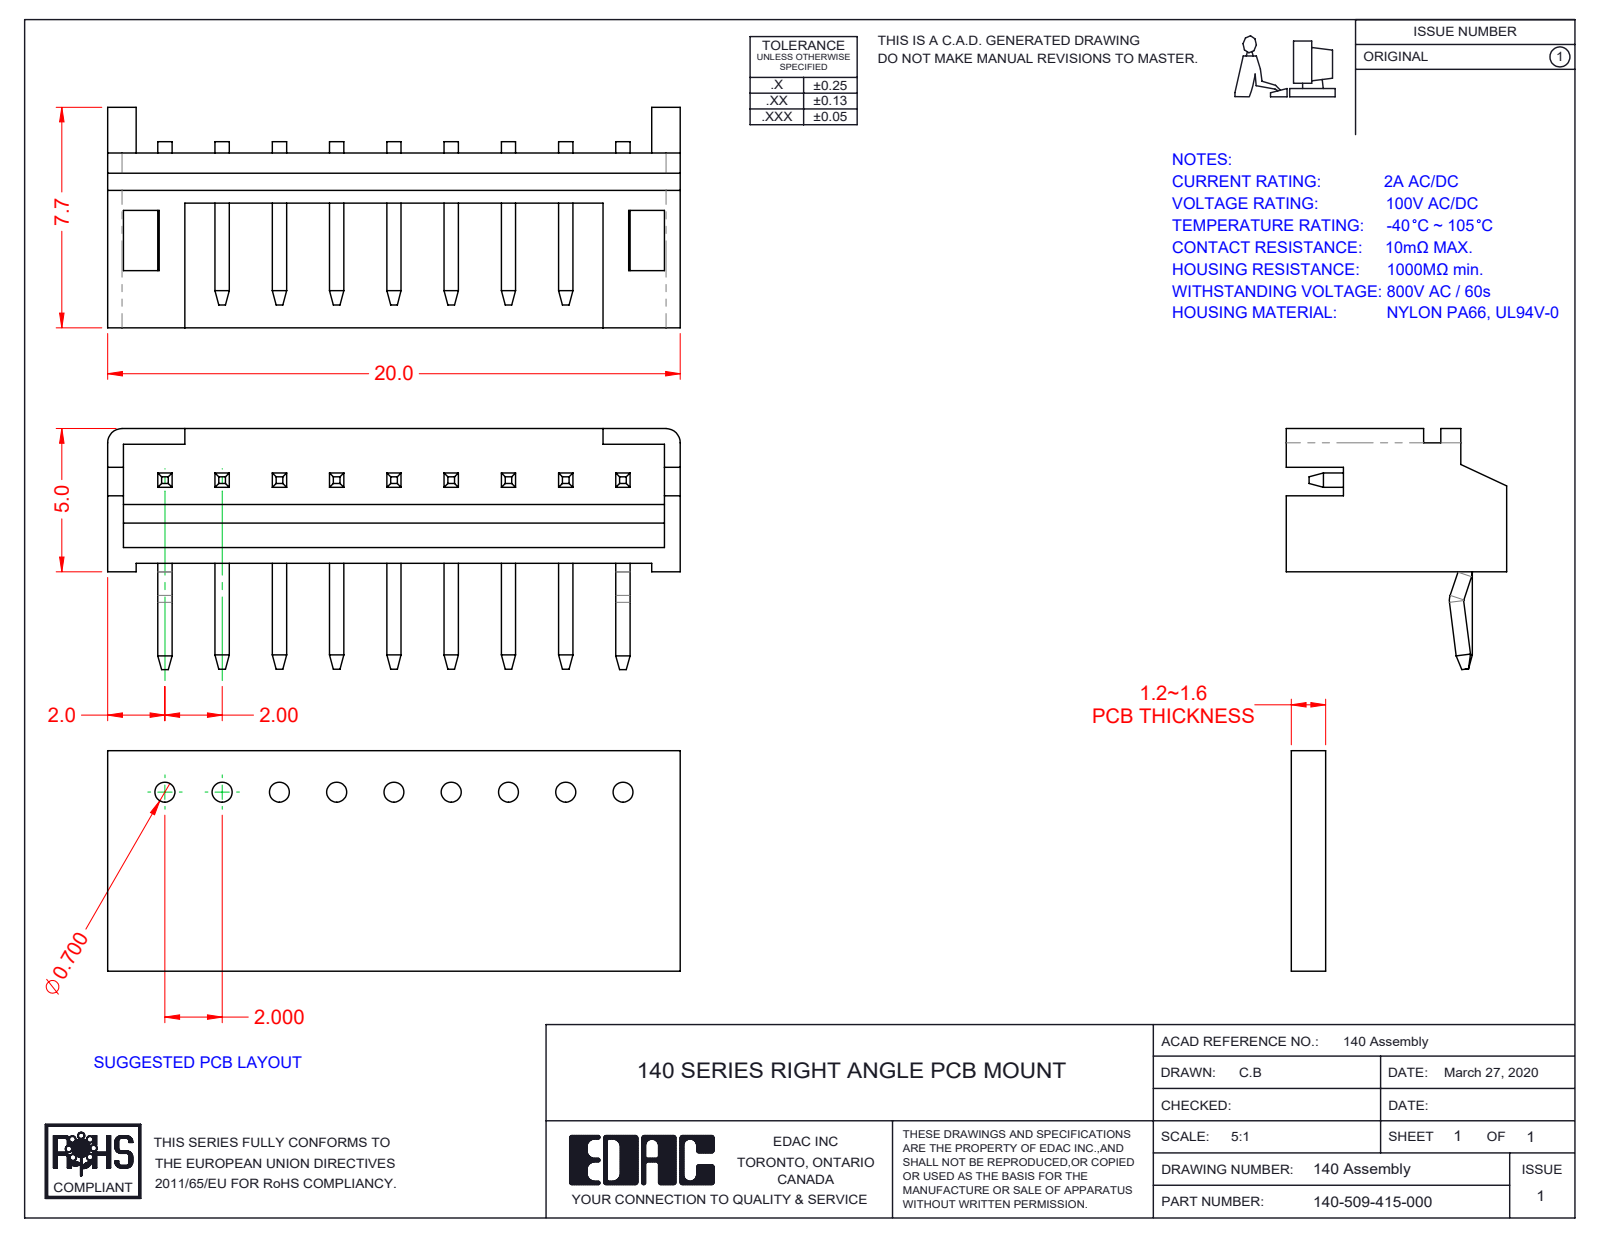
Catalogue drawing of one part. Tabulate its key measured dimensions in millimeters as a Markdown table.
| quantity | value |
| --- | --- |
| part name | RA Housing_509; 140-509-415-000; RA Contact_Str; RA Contact_Kink |
| STEP written by | SolidWorks 2016 (CONFIG_CONTROL_DESIGN) |
| units | millimeters |
| bodies | 10 solids, 349 faces (319 planar, 30 cylindrical, 0 other) |
| overall size | 20 × 8.41 × 7.7 |
| volume | 239 mm³ |
| surface area | 879 mm² |
| partial cylindrical surfaces (radius × count) | 0.5 × 2, 0.55 × 2, 0.15 × 1, 0.65 × 1 |
| main face-to-face distances | 0.55, 1.5, 0.5, 2, 4, 6, 1.75, 1, 4.15, 1.55 |
